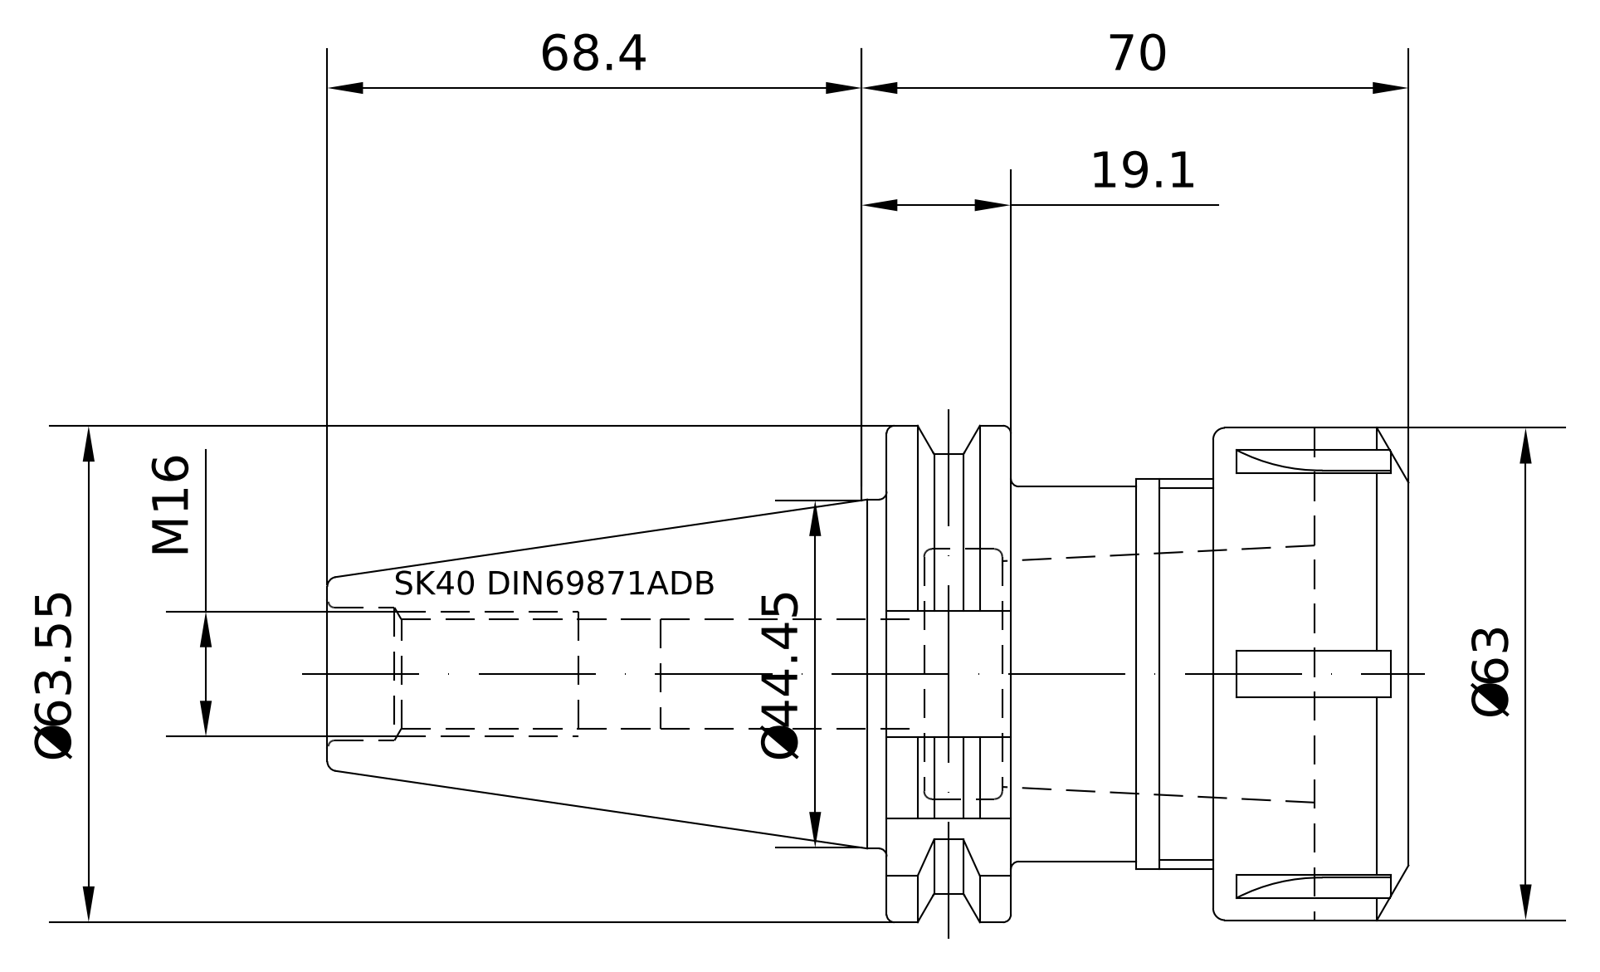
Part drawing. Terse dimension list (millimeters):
name: 40-320-40; 83-912-40; 40-320-40_ASM
written by: PRO/ENGINEER BY PARAMETRIC TECHNOLOGY CORPORATION, 2010430 (CONFIG_CONTROL_DESIGN)
unit: mm
bodies: 2 solids, 141 faces (50 planar, 34 cylindrical, 57 other)
size: 138.25 × 63.52 × 63
volume: 212 556 mm³; area: 40 253 mm²
holes: 1× ⌀13.84, 1× ⌀17.01, 1× ⌀17.5, 1× ⌀30.5
bosses: 1× ⌀63, 1× ⌀50, 1× ⌀47.5, 1× ⌀43.75, 1× ⌀16.01
rounds: 6× R2.7, 1× R1.35, 1× R28, 1× R31.76
face distances: 25.5, 41.3, 66.8, 15.85, 25.45, 50.95, 13.8, 2.05, 27.5, 53
